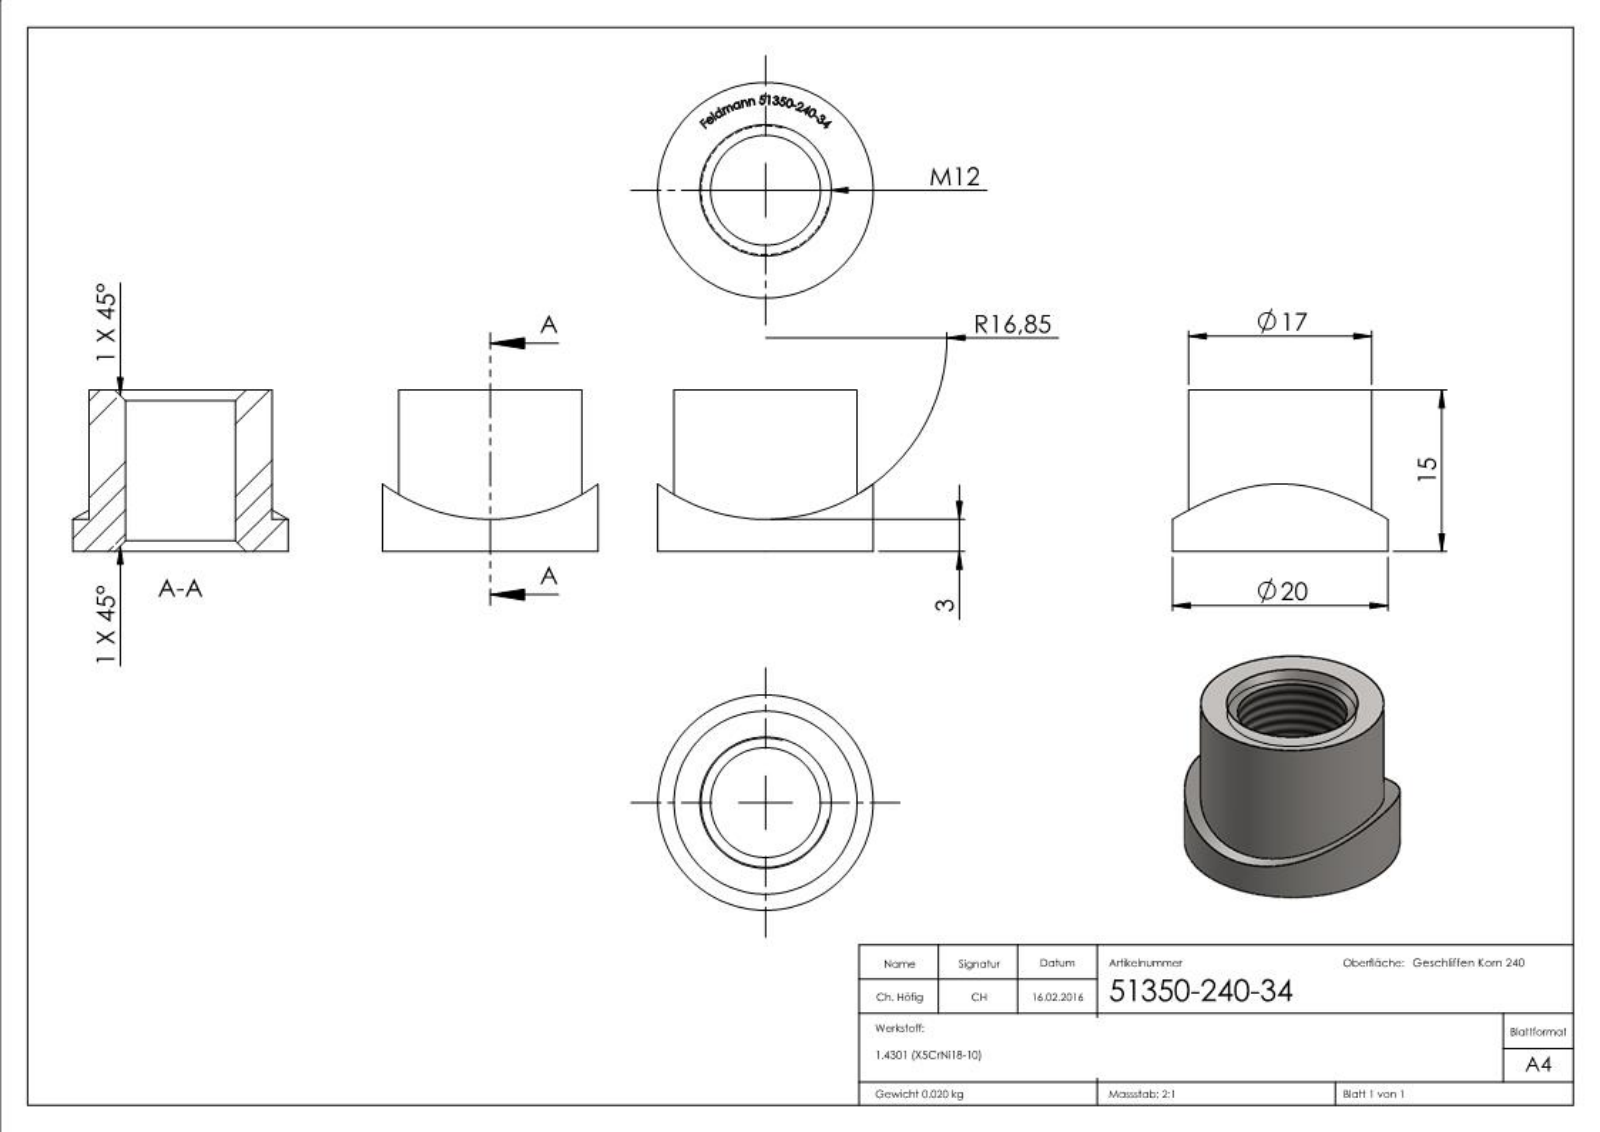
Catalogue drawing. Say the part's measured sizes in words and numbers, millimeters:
The part is named "51350-240-34". Its 3-D file was written by "SolidWorks 2015 (CONFIG_CONTROL_DESIGN)". It is 1 solid with 274 faces: 147 planar, 7 cylindrical and 120 other. Overall it measures 20 by 20 by 15 millimeters. Its volume is 2 525 cubic millimeters and its surface area 1 795 square millimeters. Round holes: 1 of diameter 10.2. Round bosses or shafts: 1 of diameter 20, 1 of diameter 17. Partial cylindrical surfaces (rounded edges, fillets, slot ends): 1 of radius 16.85. The main face-to-face distances are 15, 14.9, 0.4, 0.51, 0.43, 0.8, 0.44, 0.36, 0.47, 0.33.
